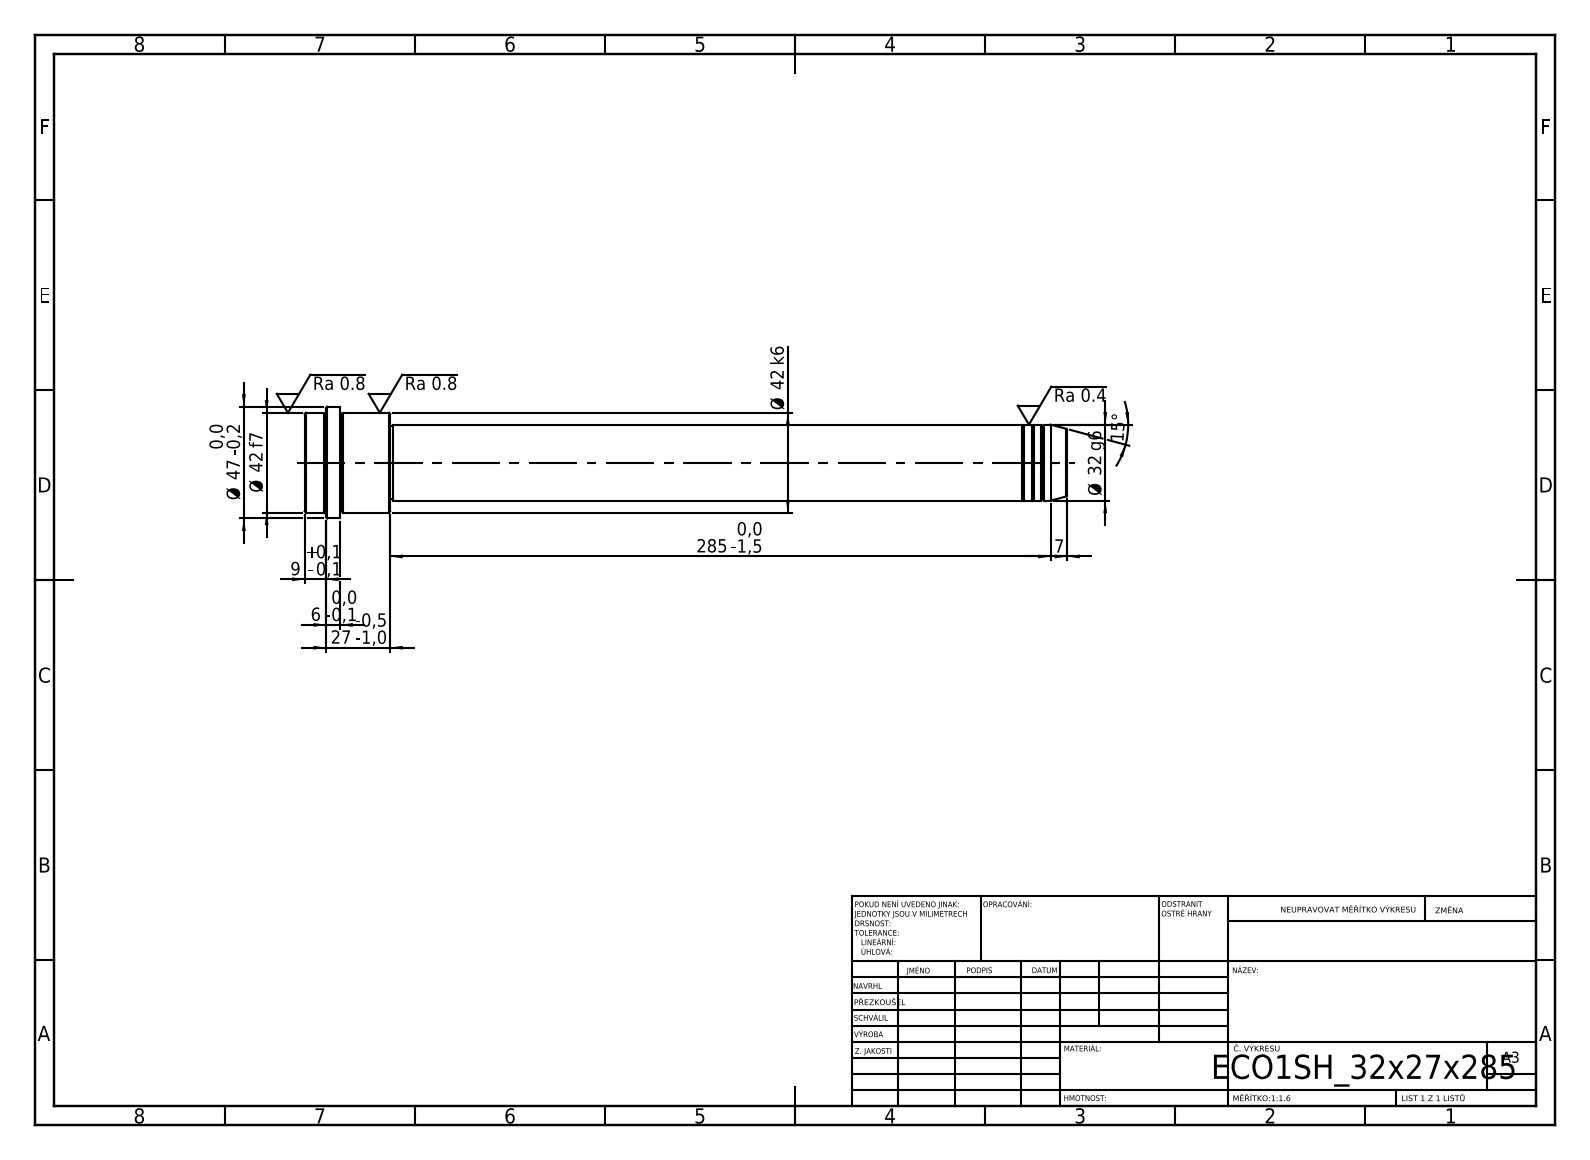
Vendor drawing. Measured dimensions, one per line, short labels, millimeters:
written by: SolidWorks 2019 (CONFIG_CONTROL_DESIGN)
unit: mm
bodies: 1 solid, 52 faces (6 planar, 16 cylindrical, 30 other)
size: 321 × 47 × 47
volume: 280 227 mm³; area: 37 041 mm²
bosses: 1× ⌀47, 1× ⌀42, 1× ⌀32, 1× ⌀31
face distances: 321, 285, 36, 306, 21, 15, 312, 27, 6, 9
